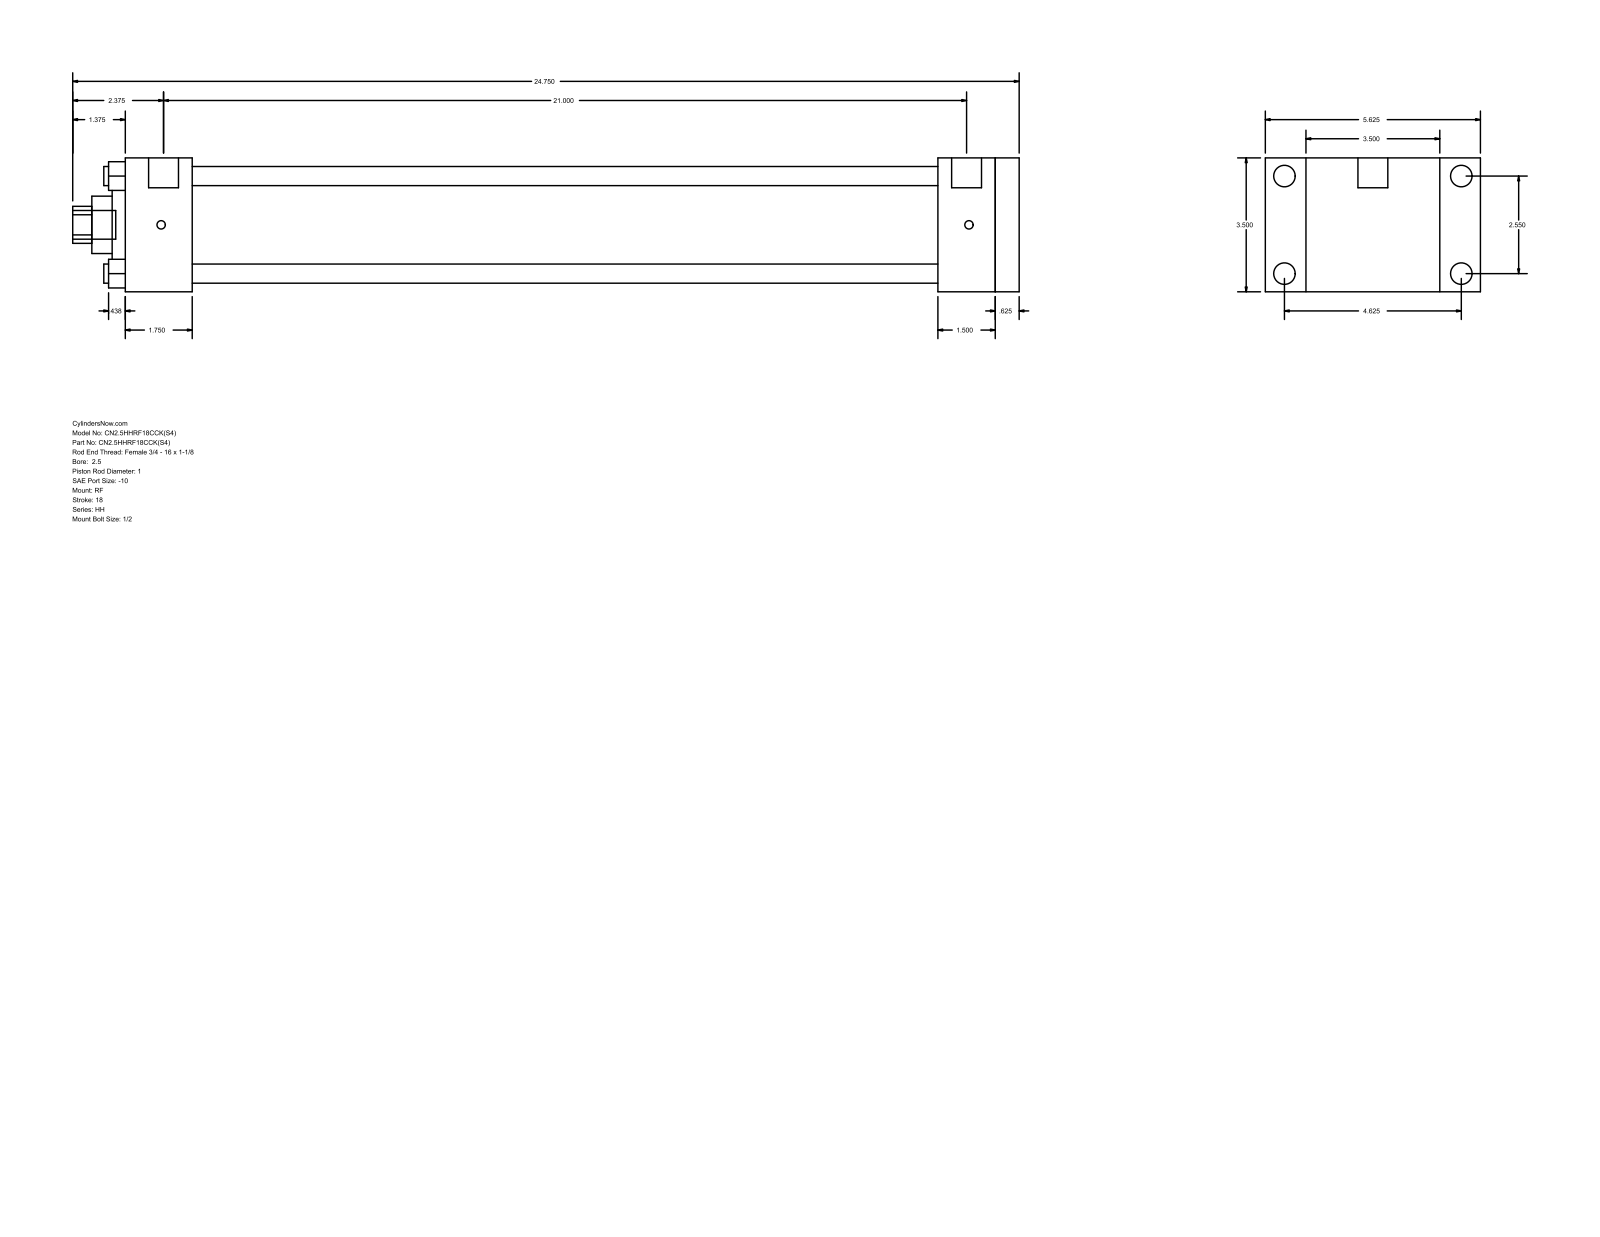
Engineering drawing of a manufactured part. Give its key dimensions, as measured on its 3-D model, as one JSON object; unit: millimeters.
{"part_name": "HH_RF__0250_1", "step_written_by": "GSSL Pune (CONFIG_CONTROL_DESIGN)", "units": "millimeters", "bodies": {"solids": 0, "faces": 94, "planar": 65, "cylindrical": 29, "other": 0}, "overall_size": [628.65, 142.88, 88.9], "round_holes": [[12.7, 4], [25.4, 1], [38.1, 1], [60.33, 1], [73.03, 1]], "round_bosses_or_shafts": [[14.3, 4], [5.56, 4], [19.84, 2], [19.05, 1]], "partial_cylinders_radius": [[12.29, 1]], "face_to_face_distances": [88.9, 15.88, 577.85, 593.73, 44.46, 533.39, 549.27, 539.75, 495.29, 38.1], "hole_center_spacings": [45.79, 64.76, 91.58]}
